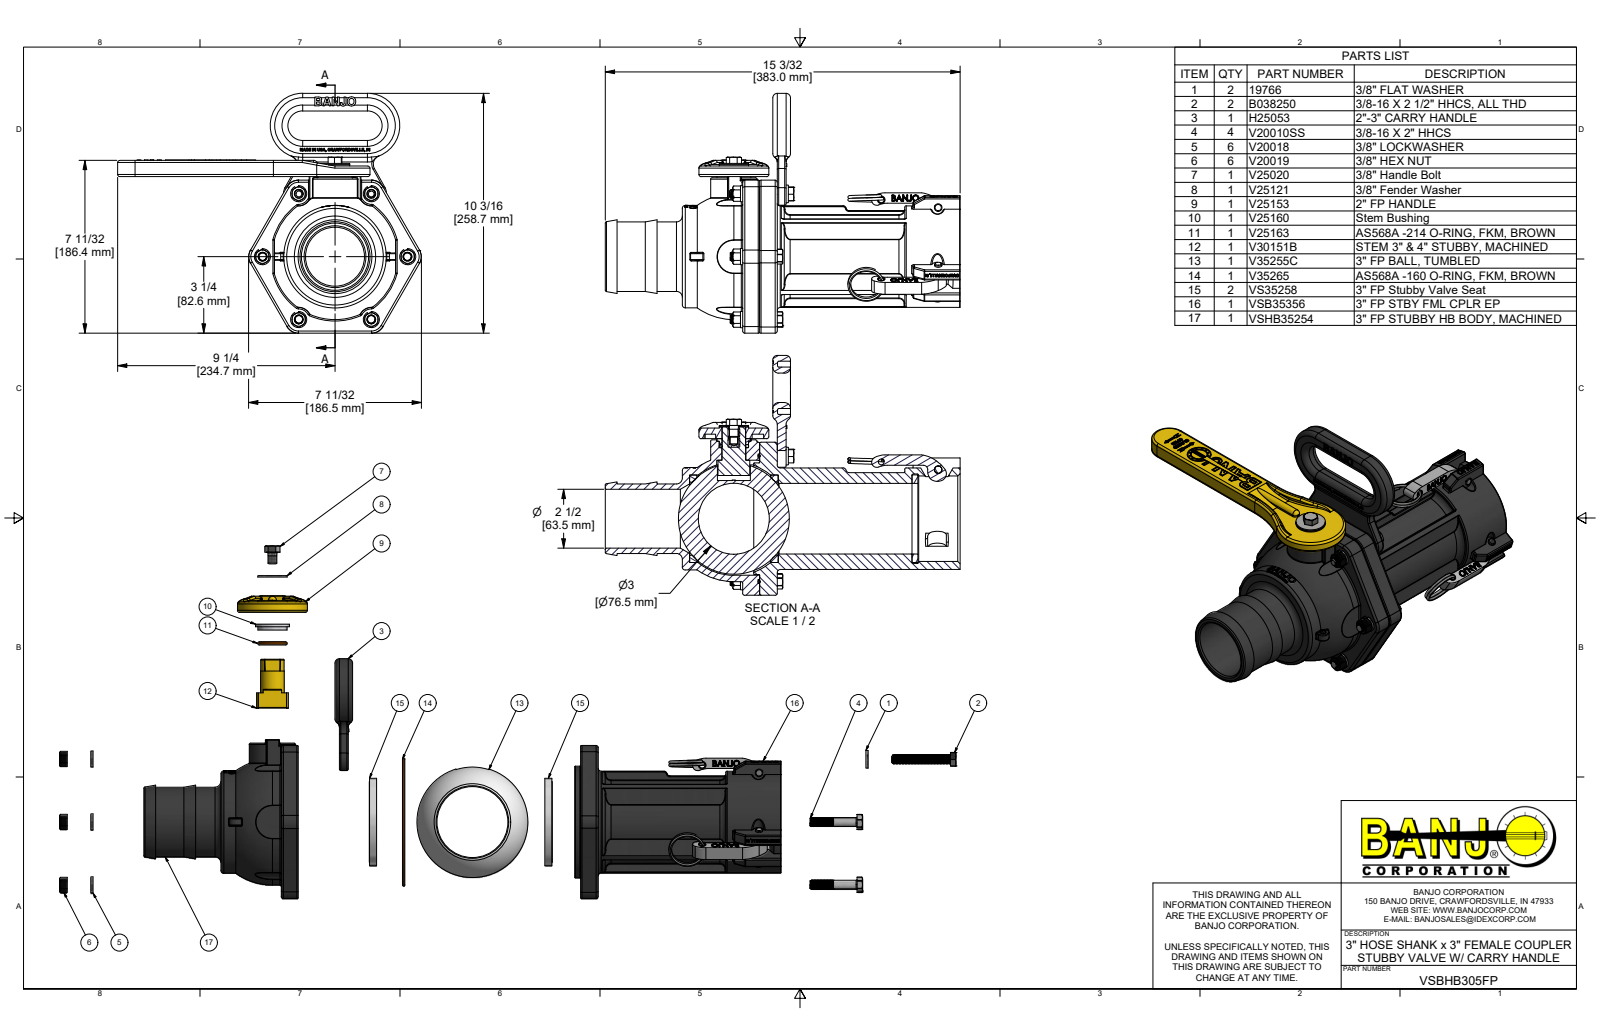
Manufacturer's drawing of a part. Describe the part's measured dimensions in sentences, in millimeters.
The part is named "VSBHB305FP; VSHB35254; VSHB35254X; VSB35356 (+8 more)". Its 3-D file was written by "Autodesk Inventor 2019 (AUTOMOTIVE_DESIGN)". It is 44 solids with 5786 faces: 1737 planar, 1668 cylindrical and 2381 other. Overall it measures 383 by 328 by 258.7 millimeters. Its volume is 2 175 000 cubic millimeters and its surface area 562 700 square millimeters. Round holes: 7 of diameter 9.5, 6 of diameter 7.8, 6 of diameter 9.8, 6 of diameter 11.4, 6 of diameter 11.7, 5 of diameter 6.4, 3 of diameter 8, 3 of diameter 8.1, 3 of diameter 10.3, 2 of diameter 7.5, 1 of diameter 7.8, 1 of diameter 17.3. Round bosses or shafts: 60 of diameter 8.2, 6 of diameter 17.4, 6 of diameter 9.5, 3 of diameter 8.3, 3 of diameter 7.9, 2 of diameter 19.1, 1 of diameter 131.1, 1 of diameter 120.4. Partial cylindrical surfaces (rounded edges, fillets, slot ends): 353 of radius 0.2, 80 of radius 0.8, 51 of radius 0.1, 32 of radius 1.5, 32 of radius 2.3, 24 of radius 1.5, 20 of radius 3.2, 8 of radius 4.1. The main face-to-face distances are 19.1, 37.3, 18.3, 165.1, 11.4, 9.5, 57.4, 145.4, 164.5, 182.8. The hole center spacings are 78.3, 78.4, 135.6, 78.1, 78.1, 135.3, 156.5, 0.3.
